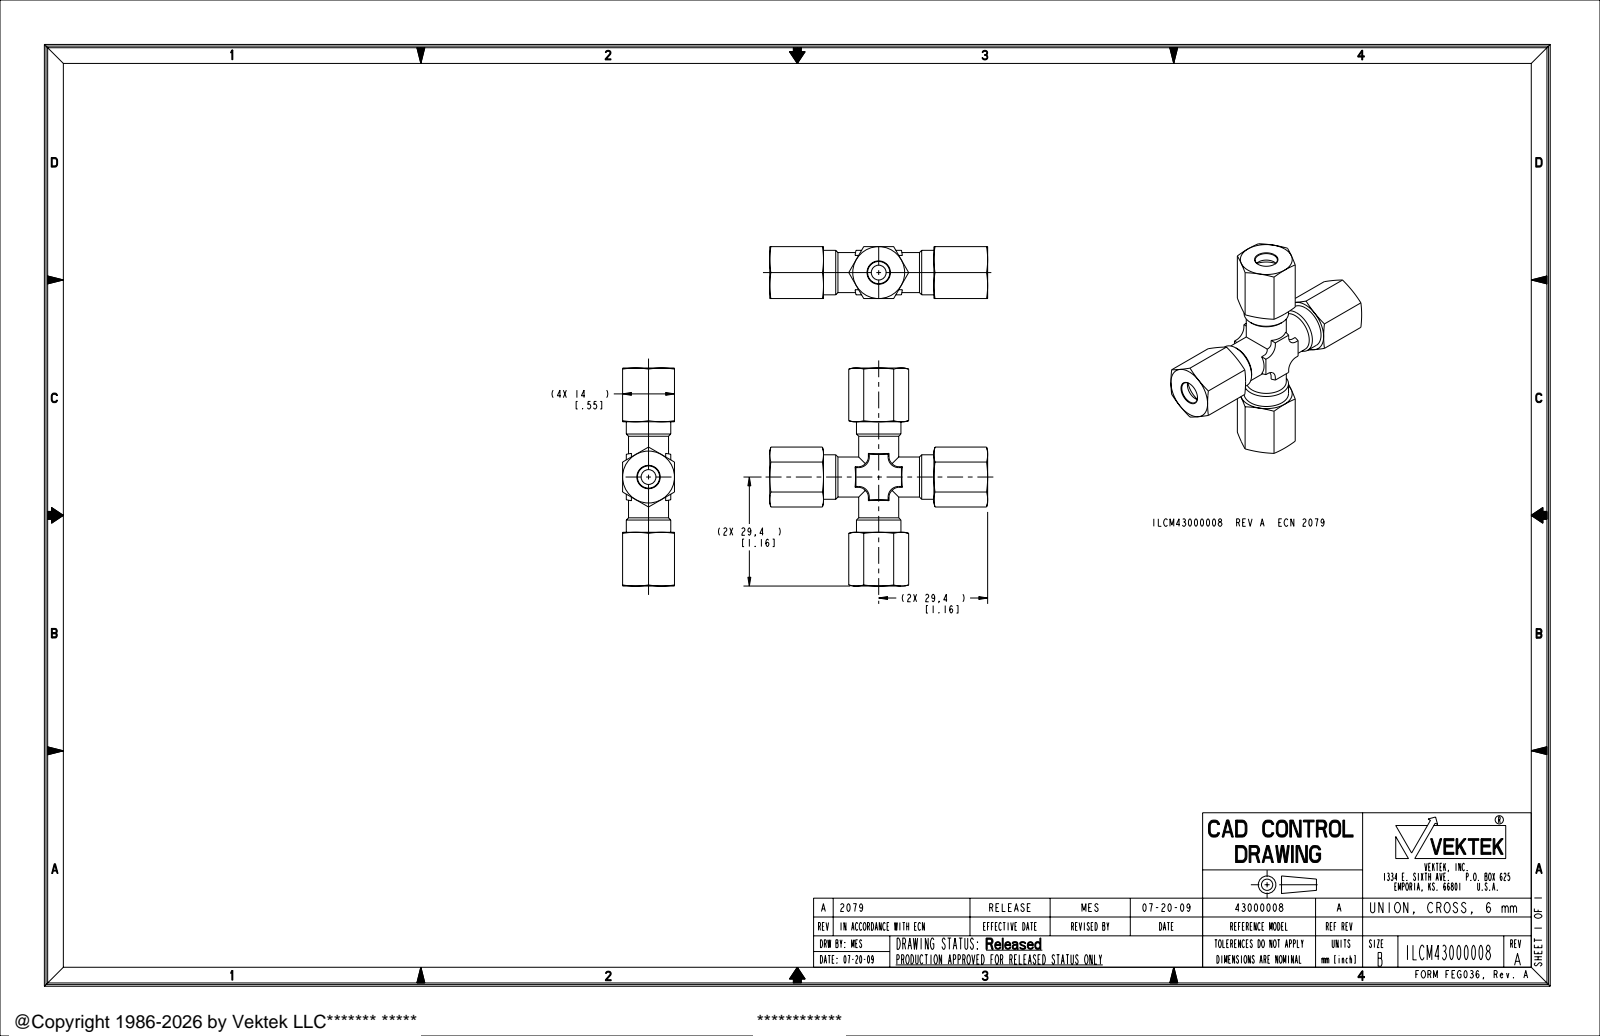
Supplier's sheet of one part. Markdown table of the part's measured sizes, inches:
| quantity | value |
| --- | --- |
| part name | ILCM43000008 |
| STEP written by | PRO/ENGINEER BY PARAMETRIC TECHNOLOGY CORPORATION, 2007460 (AUTOMOTIVE_DESIGN_CC2) |
| units | inches |
| bodies | 1 solid, 210 faces (66 planar, 48 cylindrical, 96 other) |
| overall size | 2.315 × 2.315 × 0.551 |
| volume | 0.65 in³ |
| surface area | 12.27 in² |
| round holes (diameter × count) | 0.157 × 2, 0.236 × 2, 0.409 × 2 |
| round bosses / shafts (diameter × count) | 0.472 × 2, 0.425 × 2 |
| main face-to-face distances | 0.551, 2.315, 0.039, 0.512, 0.571, 1.744, 0.409, 1.906, 0.161, 1.335 |
